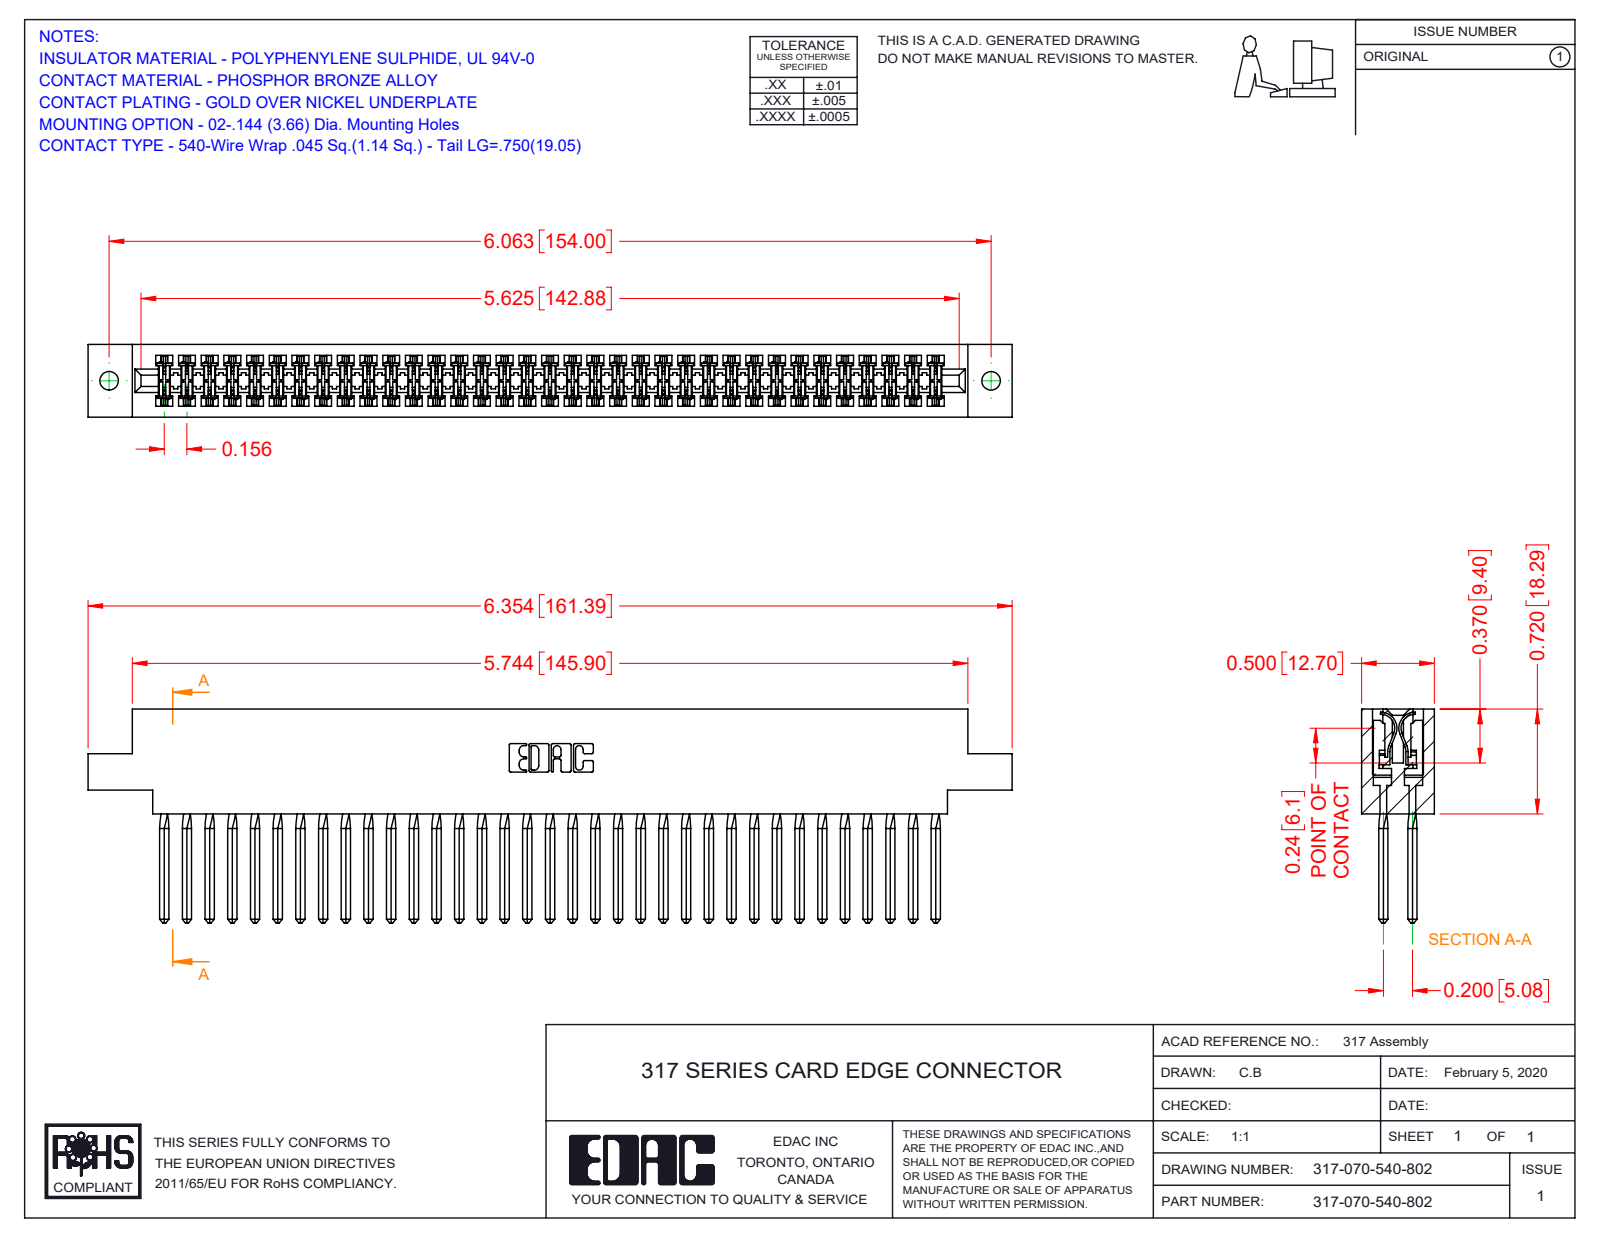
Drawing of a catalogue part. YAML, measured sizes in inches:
part_name: "317-290-001_540; 317 Part_.144 Dia; 317-070-540-802"
step_written_by: "SolidWorks 2016 (CONFIG_CONTROL_DESIGN)"
units: inches
bodies: {solids: 71, faces: 6332, planar: 5168, cylindrical: 884, other: 280}
overall_size: [6.354, 1.47, 0.5]
volume: 1.636
surface_area: 61.14
round_holes:
  - {diameter: 0.128, count: 2}
partial_cylinders:
  - {radius: 0.015, count: 140}
  - {radius: 0.01, count: 22}
  - {radius: 0.007, count: 6}
  - {radius: 0.031, count: 6}
  - {radius: 0.026, count: 3}
  - {radius: 0.095, count: 2}
  - {radius: 0.1, count: 2}
  - {radius: 0.11, count: 2}
face_to_face_distances: [0.5, 0.075, 0.425, 0.35, 0.195, 0.11, 0.094, 0.2, 0.115, 0.131]
hole_center_spacings: [6.063]
